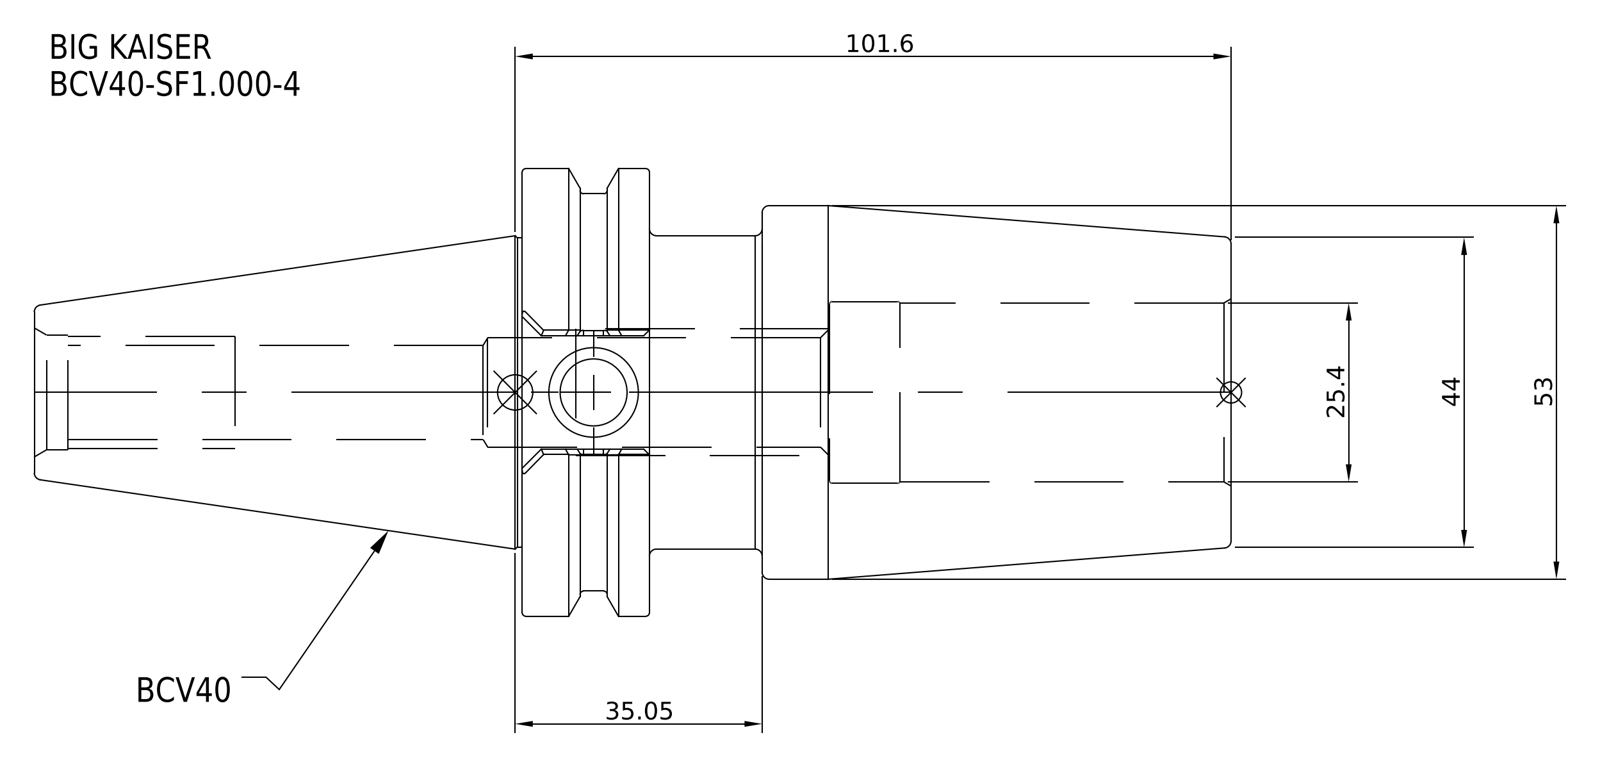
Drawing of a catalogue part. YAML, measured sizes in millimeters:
part_name: "BCV40-SF1_000-4"
step_written_by: "SolidWorks 2021 (CONFIG_CONTROL_DESIGN)"
units: millimeters
bodies: {solids: 1, faces: 30, planar: 8, cylindrical: 14, other: 8}
overall_size: [169.85, 63.5, 63.5]
volume: 248455
surface_area: 34161
round_holes:
  - {diameter: 25.4, count: 1}
round_bosses_or_shafts:
  - {diameter: 63.5, count: 1}
  - {diameter: 56.36, count: 1}
  - {diameter: 53, count: 1}
  - {diameter: 44.45, count: 1}
face_to_face_distances: [18.05, 82.55, 100.6, 66.55, 16, 34.05, 47, 19.55, 35.55, 53.6]
